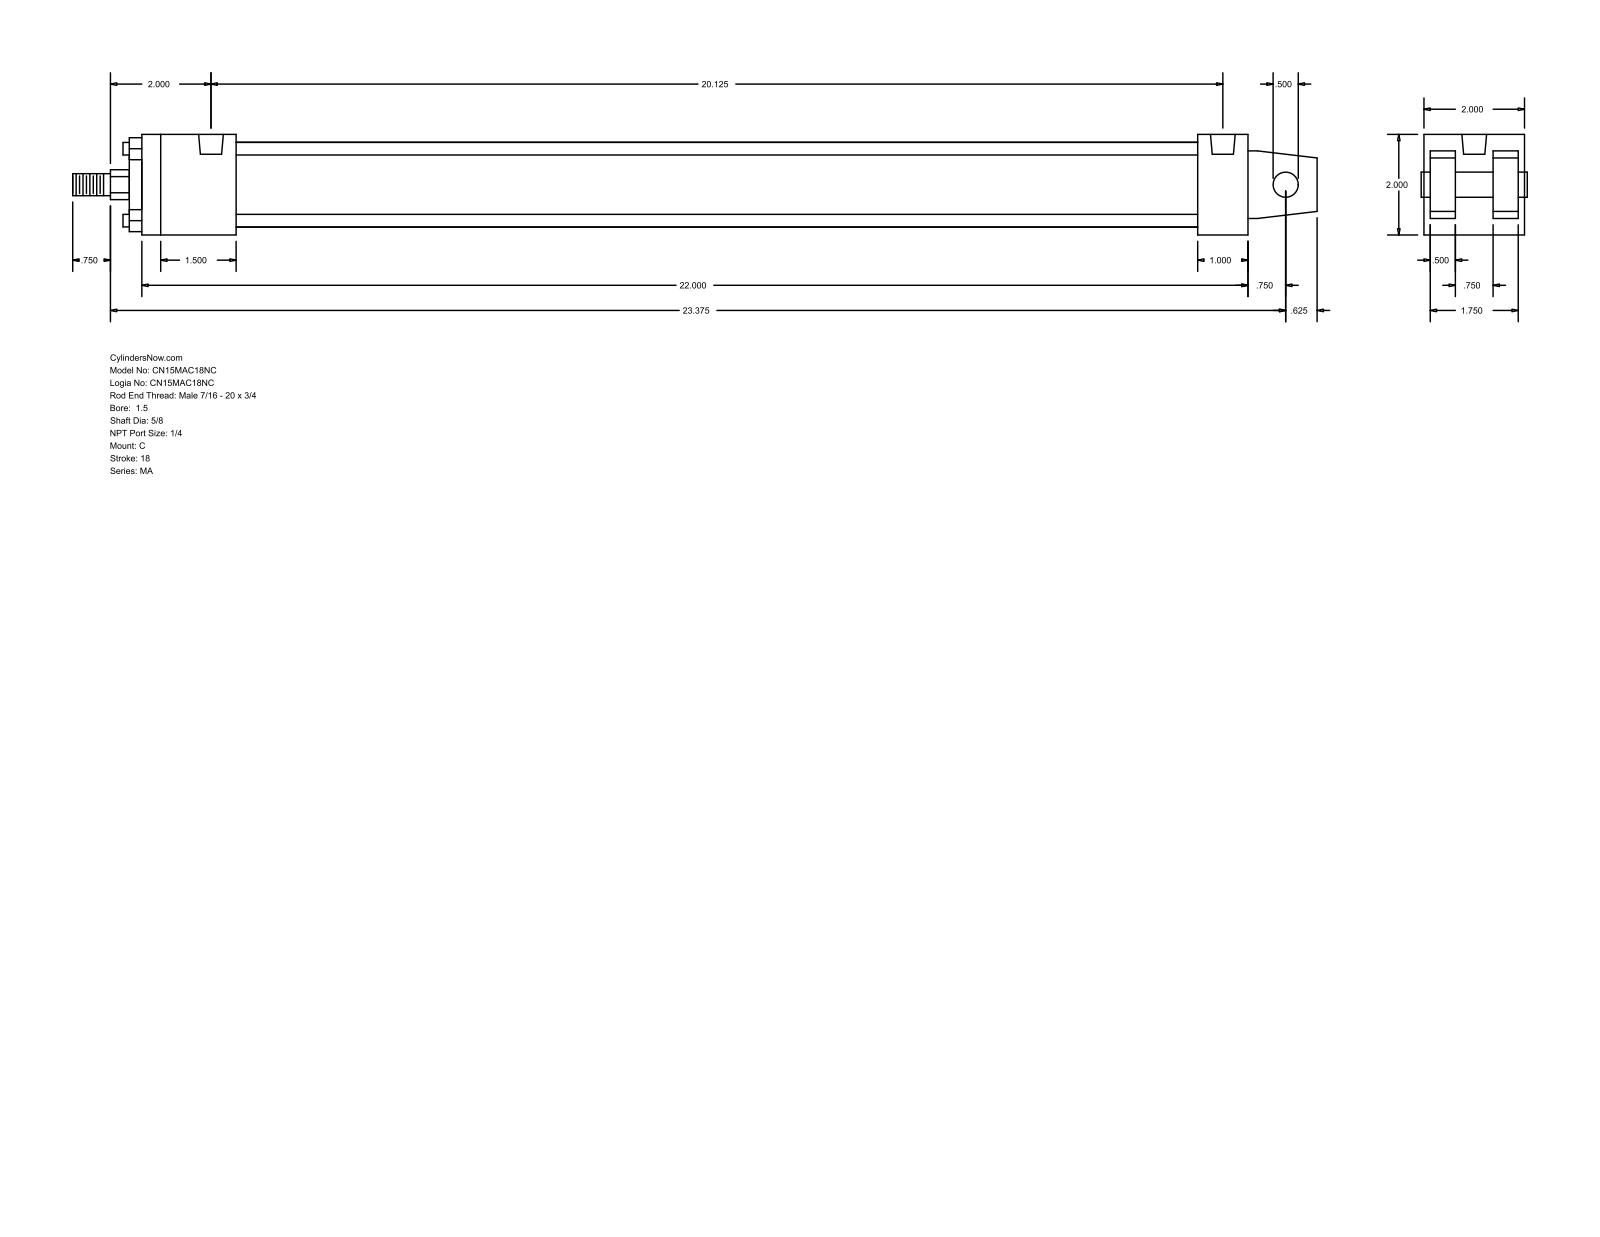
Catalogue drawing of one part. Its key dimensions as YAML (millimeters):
part_name: "MA_C__0150_0.625"
step_written_by: "GSSL Pune (CONFIG_CONTROL_DESIGN)"
units: millimeters
bodies: {solids: 0, faces: 103, planar: 76, cylindrical: 27, other: 0}
overall_size: [628.65, 50.8, 50.8]
round_holes:
  - {diameter: 7.94, count: 4}
  - {diameter: 12.49, count: 2}
round_bosses_or_shafts:
  - {diameter: 6.35, count: 4}
  - {diameter: 42.93, count: 1}
  - {diameter: 28.57, count: 1}
  - {diameter: 15.88, count: 1}
  - {diameter: 12.7, count: 1}
  - {diameter: 11.11, count: 1}
partial_cylinders:
  - {radius: 7.54, count: 1}
face_to_face_distances: [50.8, 34.93, 12.7, 15.87, 3.17, 47.63, 31.76, 558.79, 25.4, 533.39]
hole_center_spacings: [511.18]
